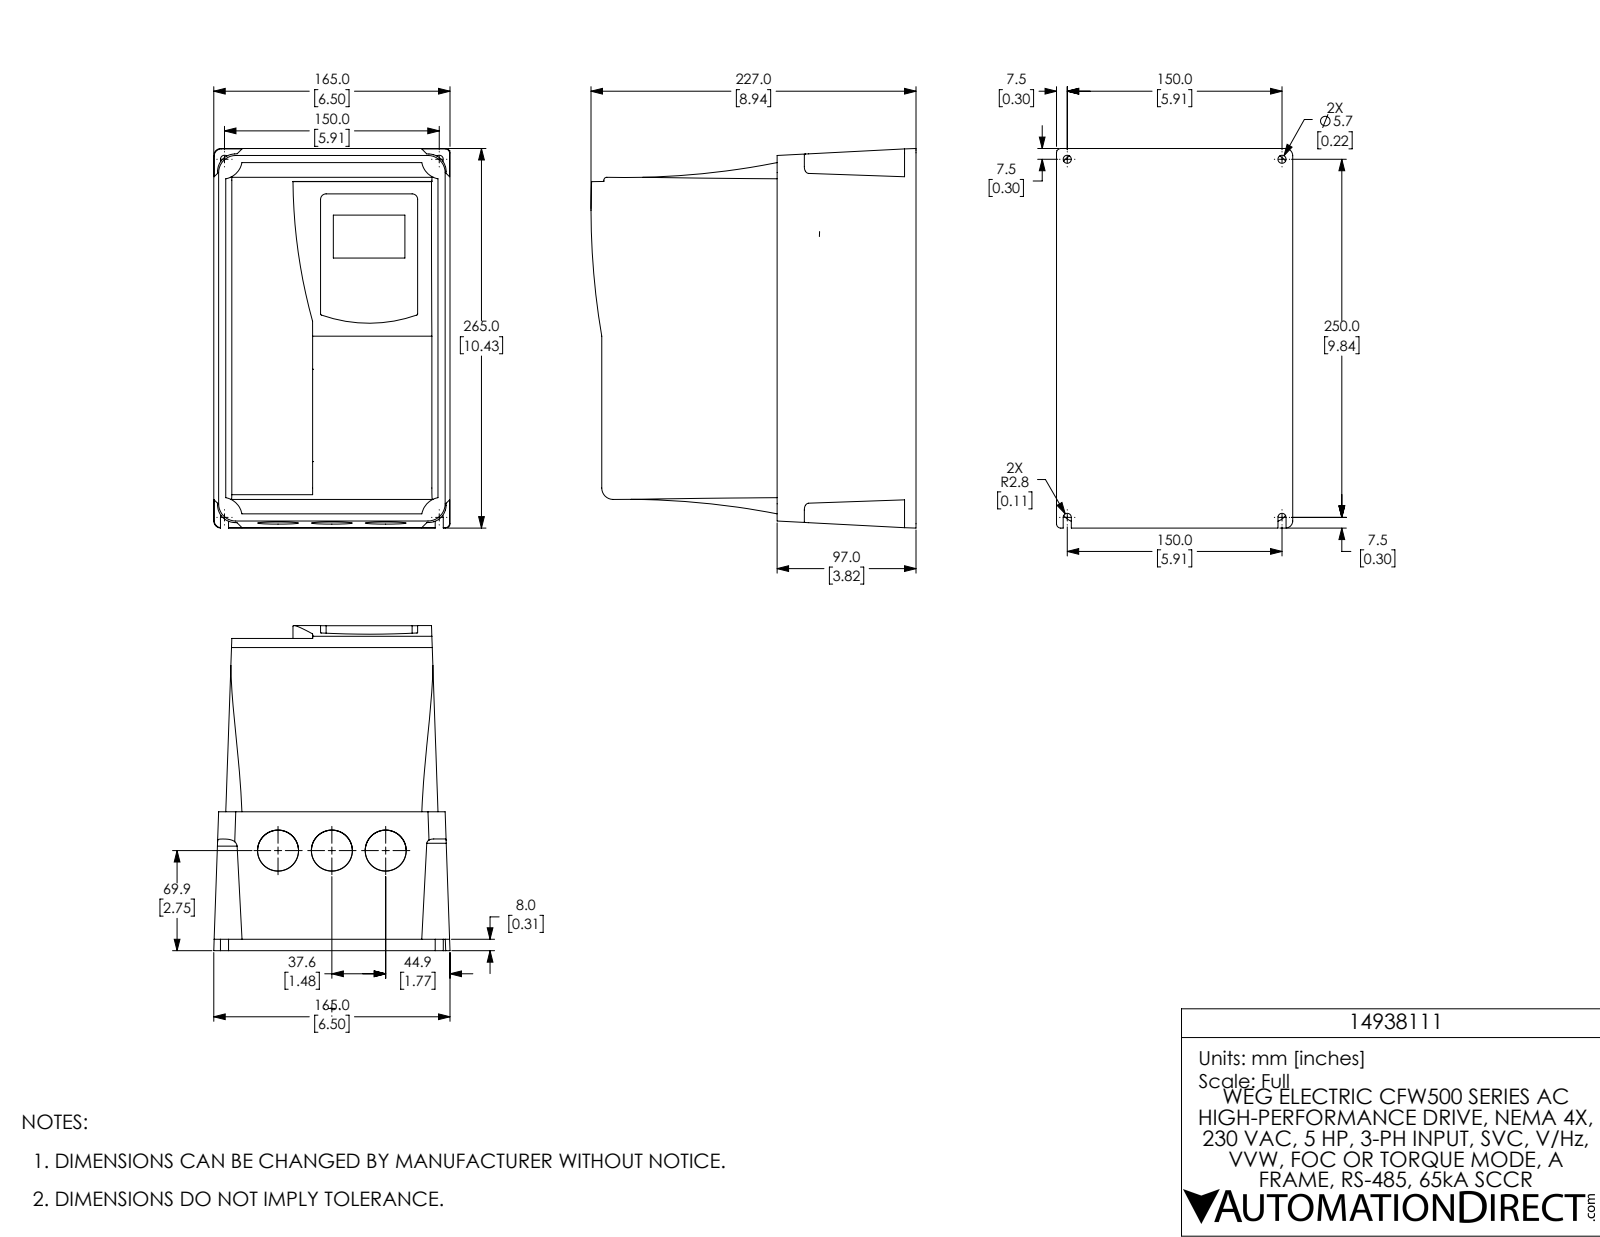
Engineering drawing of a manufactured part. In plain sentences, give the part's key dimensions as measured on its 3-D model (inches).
The part is named "CFW500 MEC-A IP66 - SEM SECCIONADORA Coord". Its 3-D file was written by "SolidWorks 2017 (AUTOMOTIVE_DESIGN)". It is 1 solid with 85 faces: 45 planar, 39 cylindrical and 1 other. Overall it measures 10.433 by 8.937 by 6.496 inches. Its volume is 493.8 cubic inches and its surface area 393.2 square inches. Round holes: 3 of diameter 1.126, 2 of diameter 0.223. Partial cylindrical surfaces (rounded edges, fillets, slot ends): 4 of radius 0.118, 4 of radius 0.472, 4 of radius 0.551, 3 of radius 0.197, 2 of radius 0.033, 2 of radius 0.111, 2 of radius 0.152, 1 of radius 0.079. The main face-to-face distances are 0.196, 8.642, 8.583, 0.059, 3.819, 4.764, 4.823, 10.855, 10.856, 8.602. The hole center spacings are 1.48, 2.961, 5.906.
